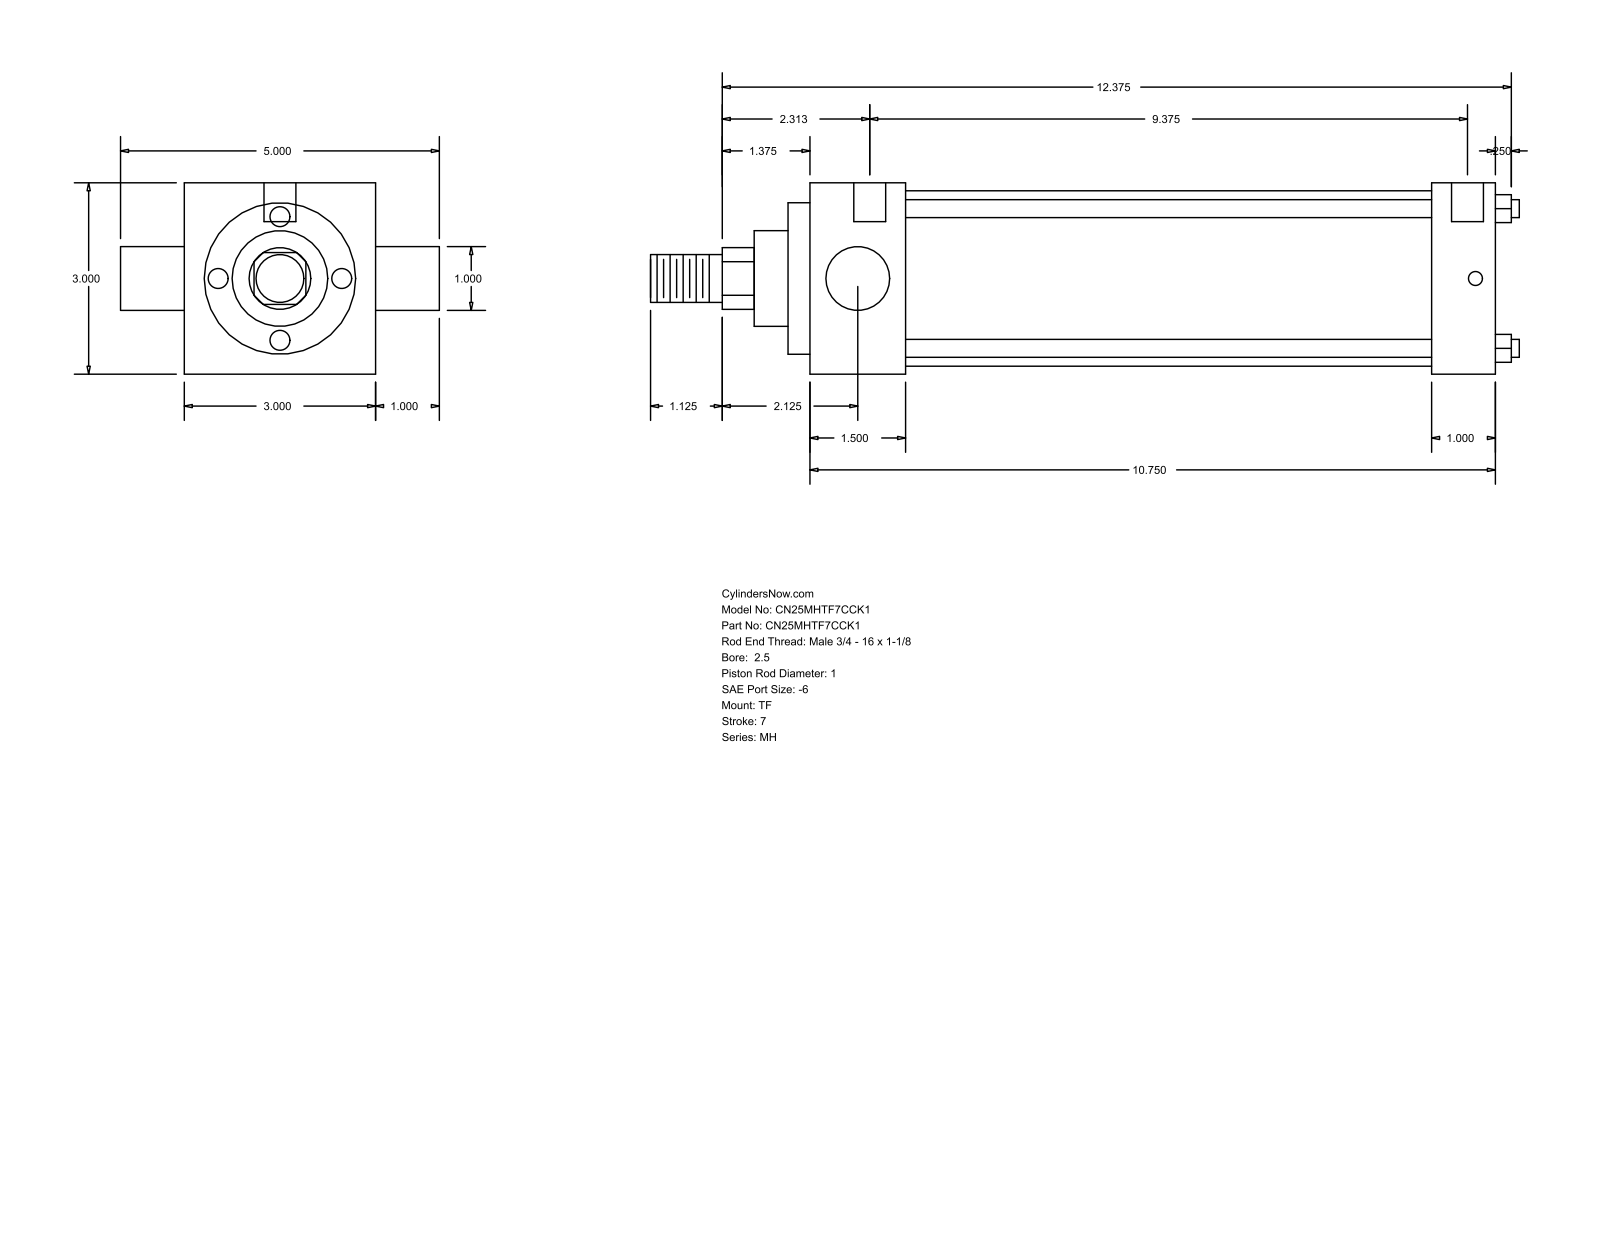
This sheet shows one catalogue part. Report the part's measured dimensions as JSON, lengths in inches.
{"part_name": "MH_TF__0250_1", "step_written_by": "GSSL Pune (CONFIG_CONTROL_DESIGN)", "units": "inches", "bodies": {"solids": 0, "faces": 86, "planar": 61, "cylindrical": 25, "other": 0}, "overall_size": [13.625, 5, 3], "round_holes": [[0.219, 3], [0.5, 2]], "round_bosses_or_shafts": [[0.281, 4], [1, 2], [2.75, 1], [2.375, 1], [1.5, 1], [0.75, 1]], "partial_cylinders_radius": [[0.484, 1]], "face_to_face_distances": [3, 10.75, 1.5, 9.25, 9.75, 8.25, 1, 0.344, 1.844, 10.094], "hole_center_spacings": [0.125, 0.187, 9.375, 9.5, 9.562, 9.687]}
